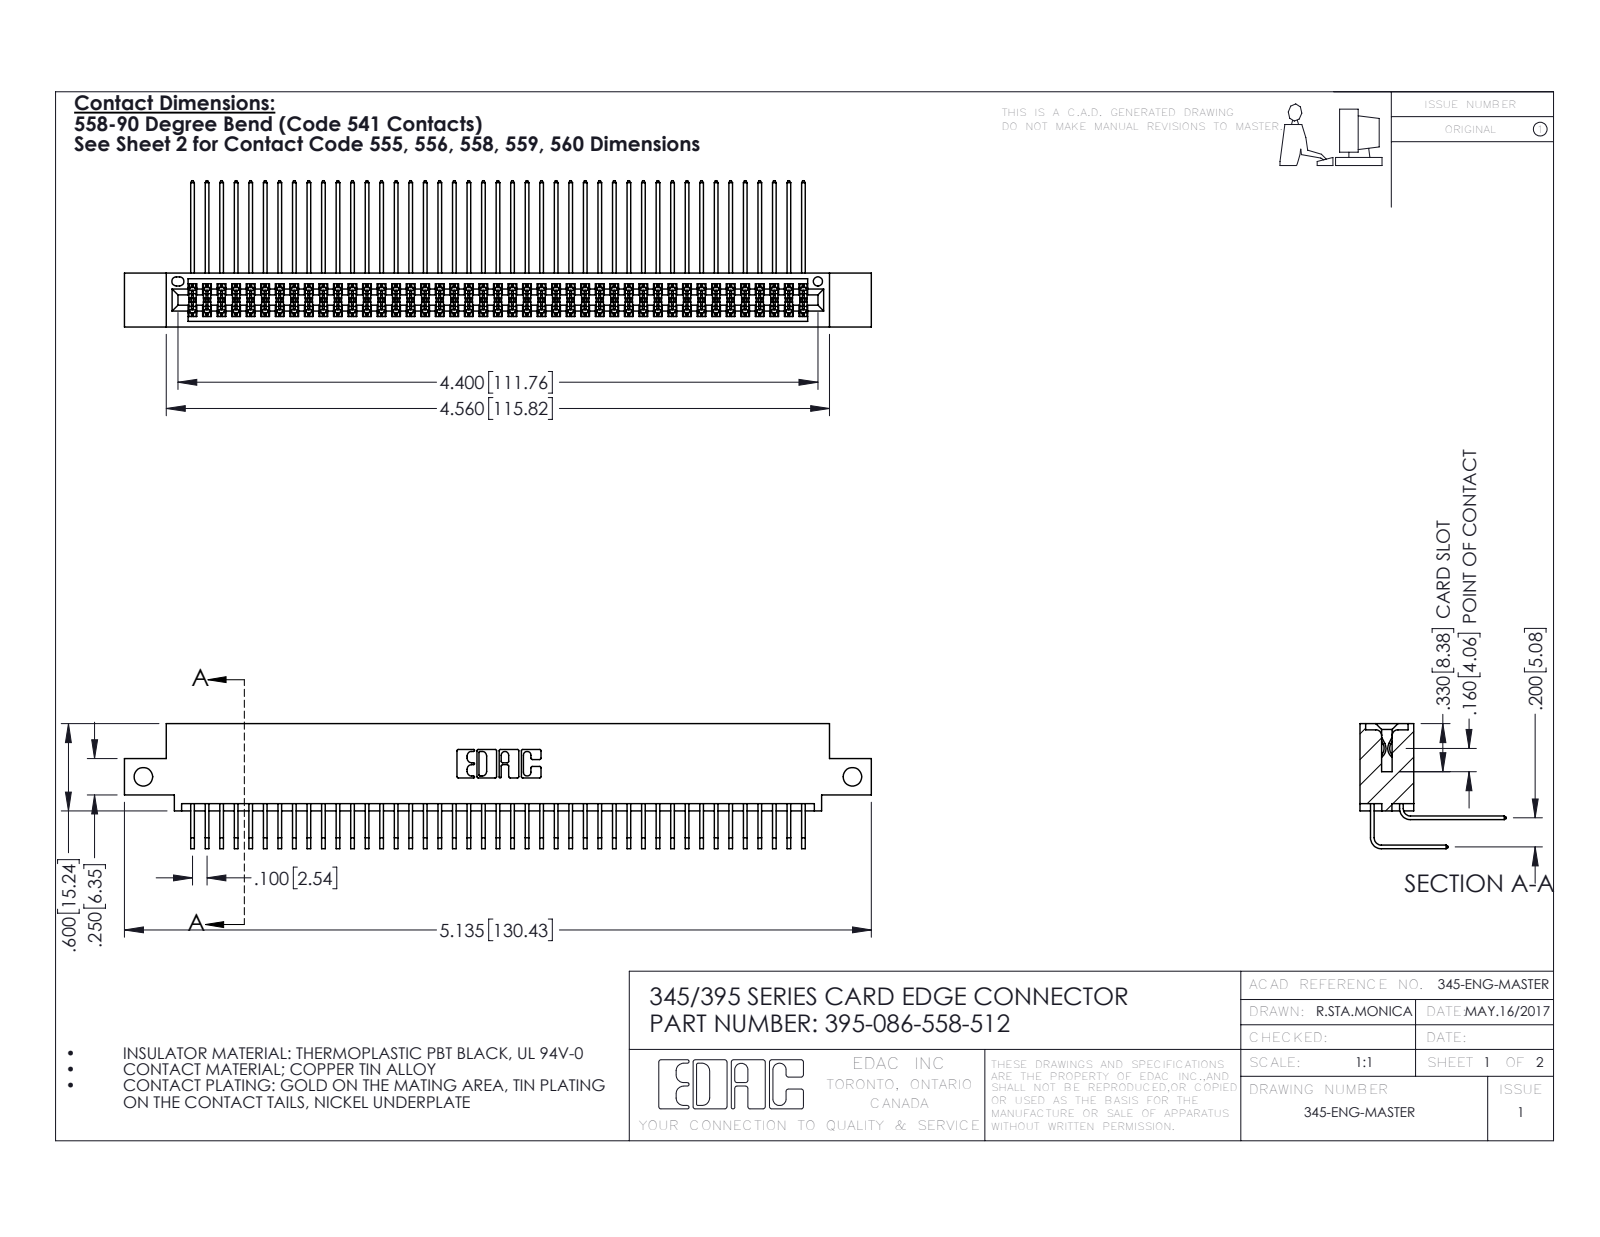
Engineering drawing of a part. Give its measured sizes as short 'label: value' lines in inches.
name: 345 Part_0.110 Offset - Side Mount; 395-086-558-512; 345-292-001_558 Tail - 2; 345-292-001_558 559 Tail - 1
written by: SolidWorks 2016 (CONFIG_CONTROL_DESIGN)
unit: in
bodies: 87 solids, 4602 faces (3094 planar, 1508 cylindrical, 0 other)
size: 5.135 × 1.005 × 0.859
volume: 0.794 in³; area: 33.4 in²
holes: 2× ⌀0.128, 1× ⌀0.064
rounds: 130× R0.006, 22× R0.01, 6× R0.007, 6× R0.031, 3× R0.026, 2× R0.014, 2× R0.019, 2× R0.022
face distances: 0.072, 0.298, 0.2, 0.37, 0.098, 0.272, 0.025, 0.225, 0.025, 0.175
hole spacings: 4.875
